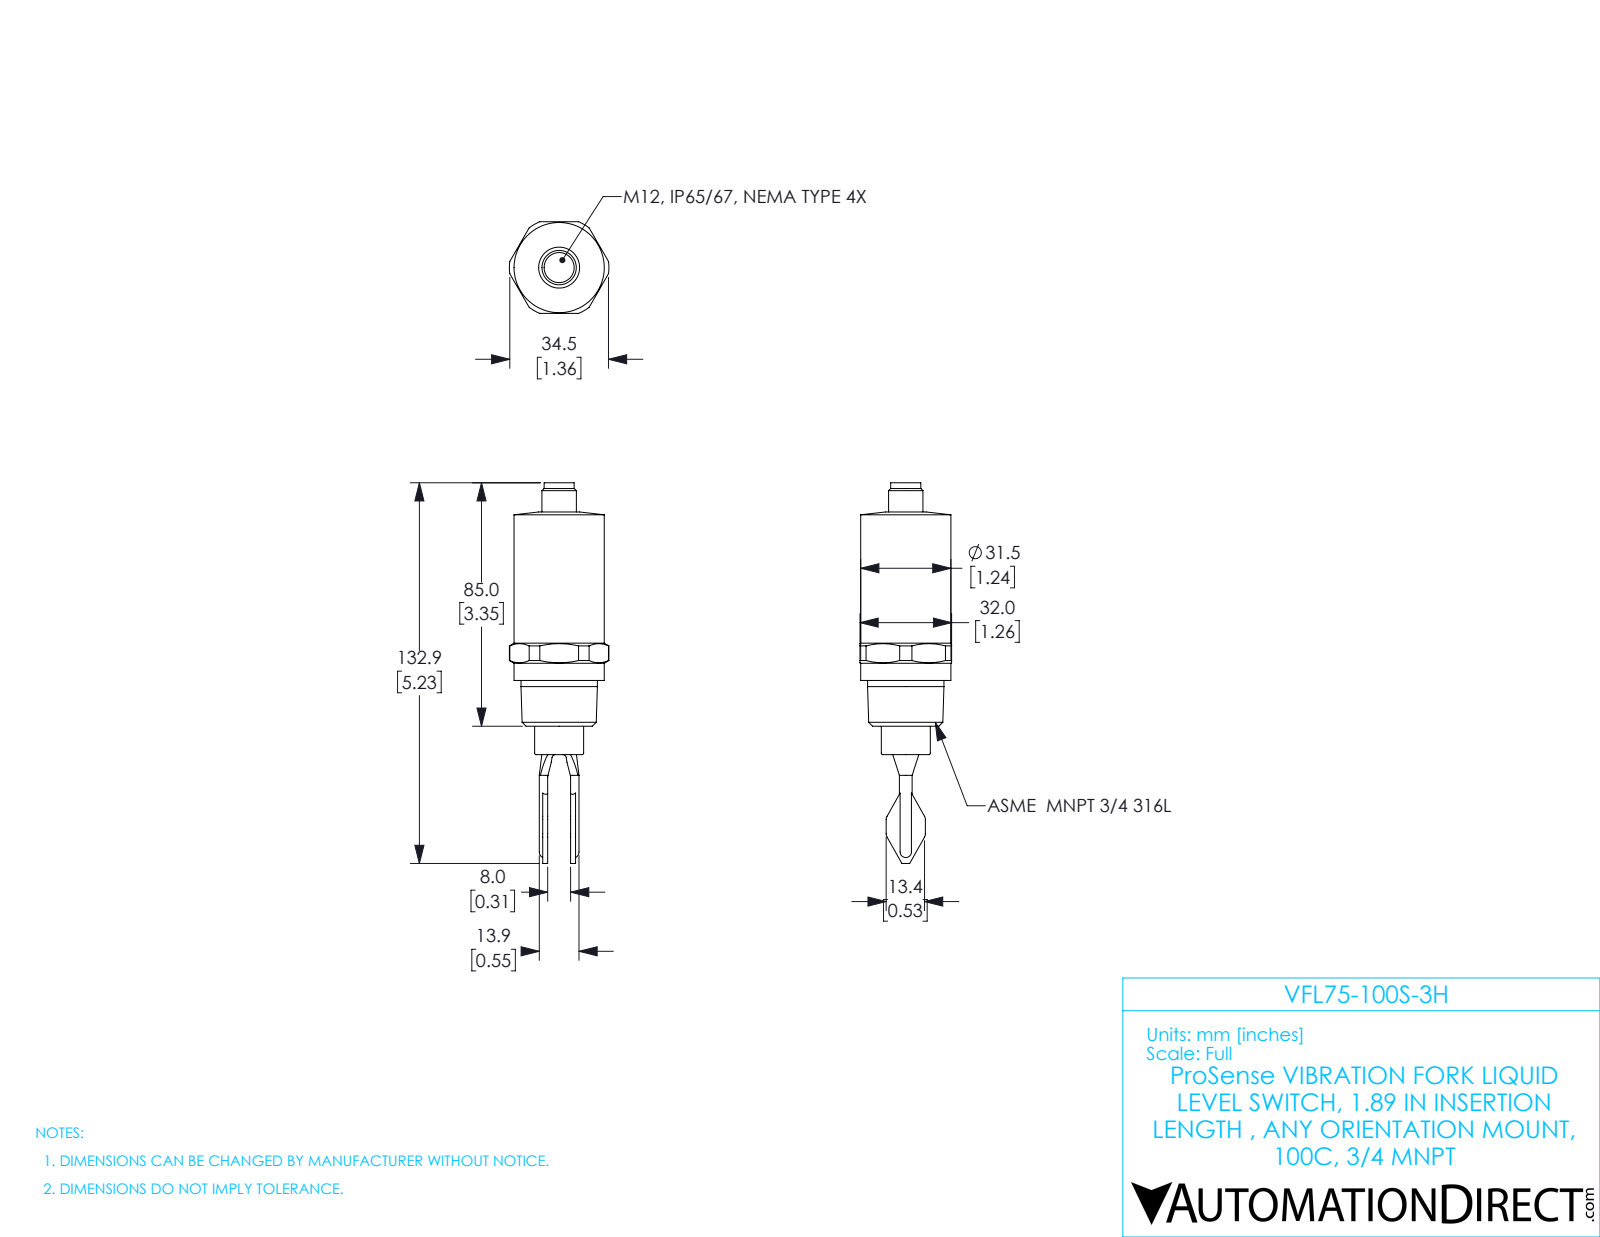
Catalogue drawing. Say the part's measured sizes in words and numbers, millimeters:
The part is named "VFL75-100S-3H". Its 3-D file was written by "SolidWorks 2017 (AUTOMOTIVE_DESIGN)". It is 1 solid with 98 faces: 45 planar, 34 cylindrical and 19 other. Overall it measures 132.9 by 34.7 by 32 millimeters. Its volume is 59 470 cubic millimeters and its surface area 11 120 square millimeters. Round bosses or shafts: 1 of diameter 31.5, 1 of diameter 26.7, 1 of diameter 17.1, 1 of diameter 12, 1 of diameter 10.5. Partial cylindrical surfaces (rounded edges, fillets, slot ends): 4 of radius 1.2, 4 of radius 2.4, 2 of radius 2.2, 1 of radius 17.4. The main face-to-face distances are 1.7, 9.7, 8, 32, 16, 11.5, 9.9, 25.9, 94.9, 85.
